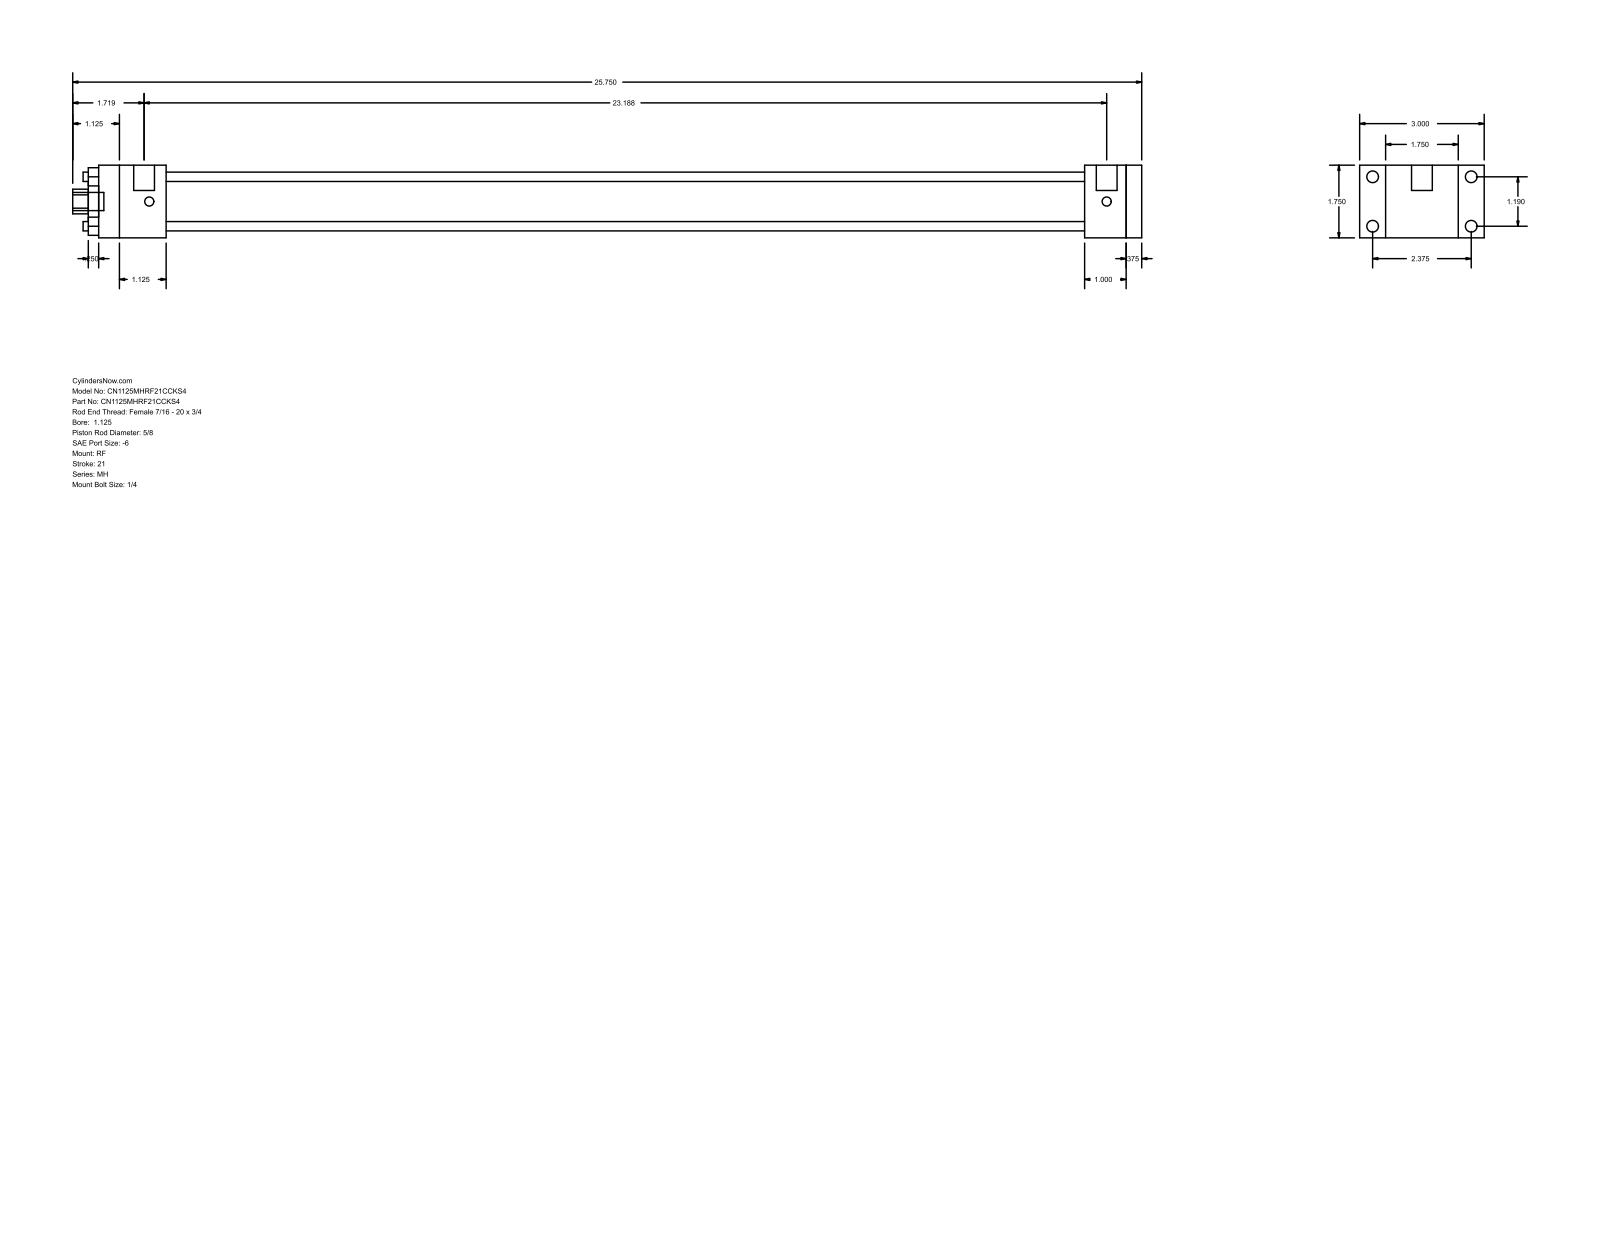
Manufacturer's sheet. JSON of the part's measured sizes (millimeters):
{"part_name": "MH_RF__0112_0.625", "step_written_by": "GSSL Pune (CONFIG_CONTROL_DESIGN)", "units": "millimeters", "bodies": {"solids": 0, "faces": 92, "planar": 64, "cylindrical": 28, "other": 0}, "overall_size": [654.05, 76.2, 44.45], "round_holes": [[5.71, 4], [15.88, 1], [28.57, 1], [34.92, 1]], "round_bosses_or_shafts": [[7.14, 4], [5.56, 4], [12.7, 2], [11.11, 1]], "partial_cylinders_radius": [[7.54, 1]], "face_to_face_distances": [44.46, 9.53, 638.17, 15.87, 587.37, 596.9, 561.97, 25.4, 34.93, 41.27], "hole_center_spacings": [21.37, 30.22, 42.74]}
